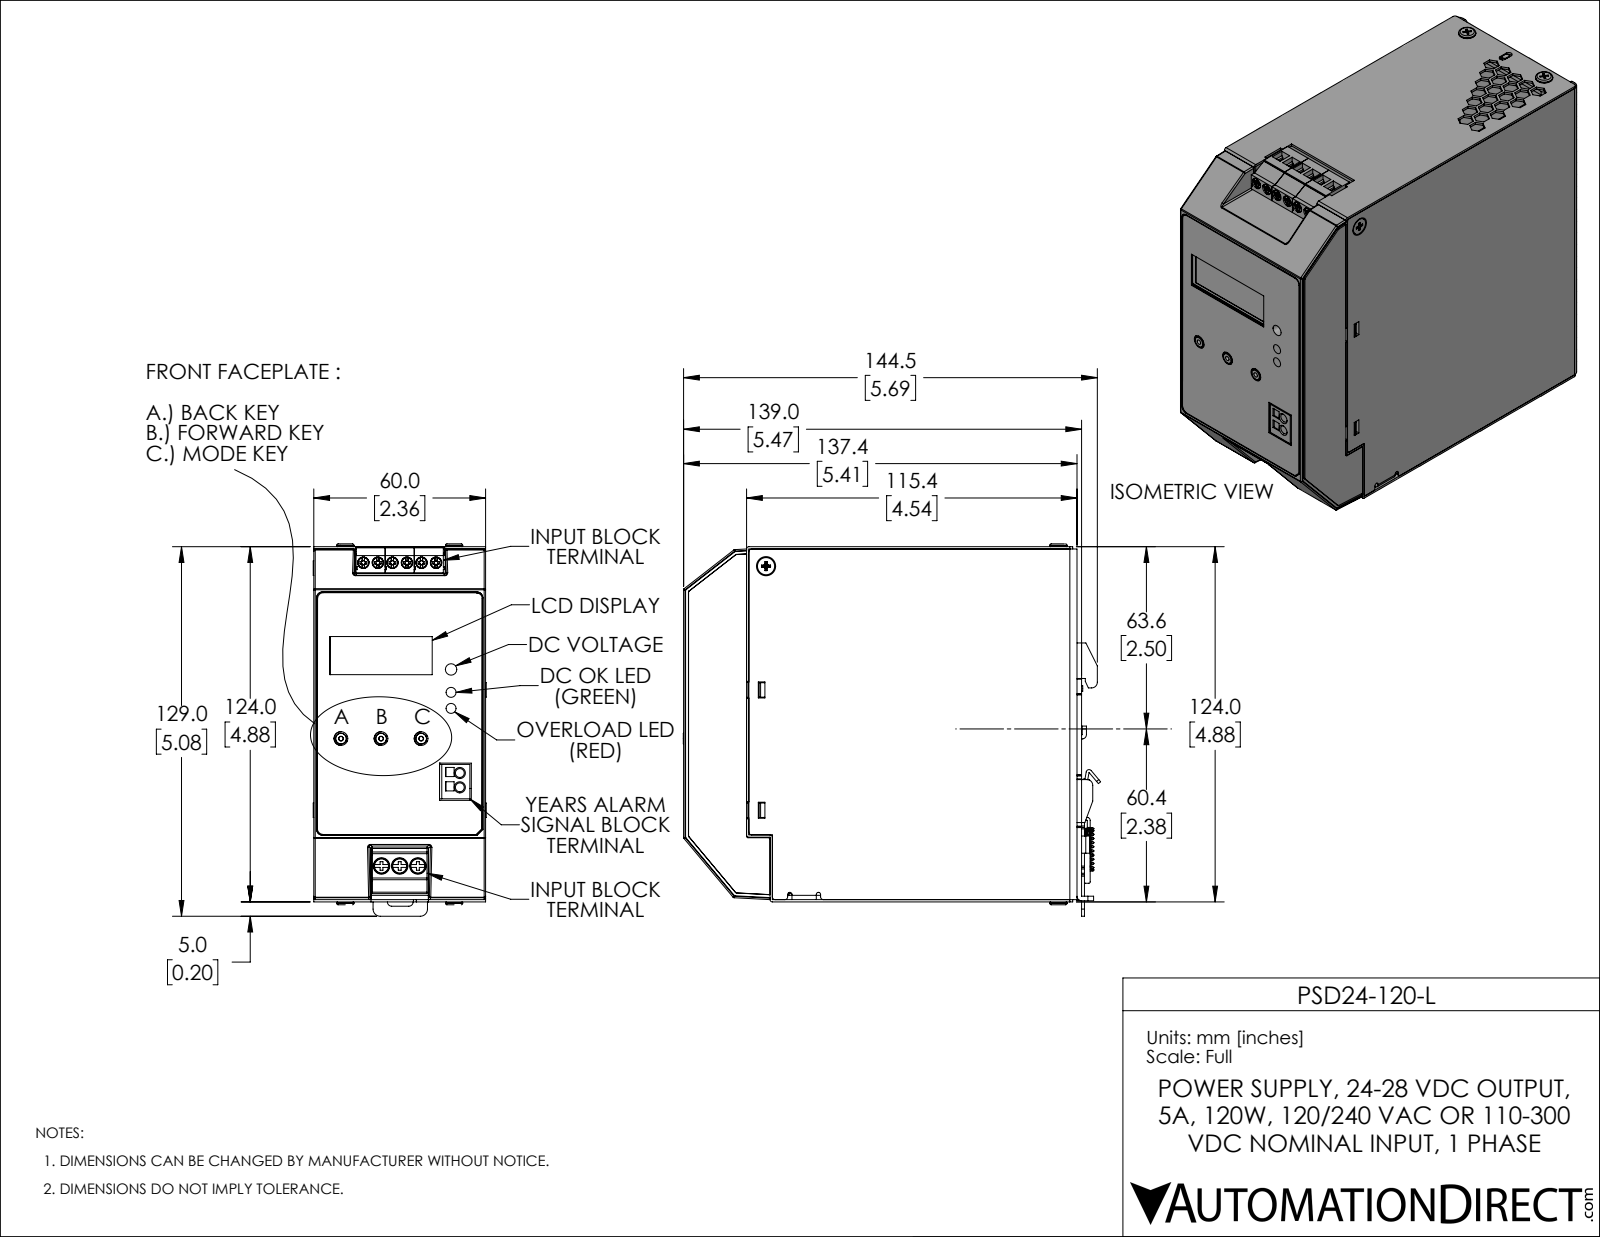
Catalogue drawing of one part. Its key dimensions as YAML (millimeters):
part_name: "PSD24-120-L"
step_written_by: "SolidWorks 2019 (AUTOMOTIVE_DESIGN)"
units: millimeters
bodies: {solids: 31, faces: 2937, planar: 2114, cylindrical: 456, other: 367}
overall_size: [145.7, 130, 60.4]
volume: 129000
surface_area: 204300
round_holes:
  - {diameter: 4, count: 8}
  - {diameter: 3.5, count: 6}
  - {diameter: 3.9, count: 5}
  - {diameter: 2.5, count: 4}
  - {diameter: 4.8, count: 3}
  - {diameter: 4.9, count: 3}
  - {diameter: 1, count: 2}
  - {diameter: 3.7, count: 1}
  - {diameter: 3.8, count: 1}
round_bosses_or_shafts:
  - {diameter: 3.9, count: 6}
  - {diameter: 5.5, count: 4}
  - {diameter: 5.7, count: 3}
  - {diameter: 6, count: 2}
  - {diameter: 4, count: 2}
  - {diameter: 2, count: 2}
  - {diameter: 3.5, count: 1}
partial_cylinders:
  - {radius: 0.5, count: 96}
  - {radius: 0.3, count: 60}
  - {radius: 1, count: 43}
  - {radius: 0.2, count: 14}
  - {radius: 0.8, count: 11}
  - {radius: 0.1, count: 8}
  - {radius: 1.5, count: 6}
  - {radius: 1.6, count: 6}
face_to_face_distances: [1.5, 58.5, 0.8, 60, 0.4, 57, 58.1, 56.6, 1.9, 123.2]
hole_center_spacings: [5.1, 10.2, 15.2, 32.7, 6.4, 9, 14, 14.1]
